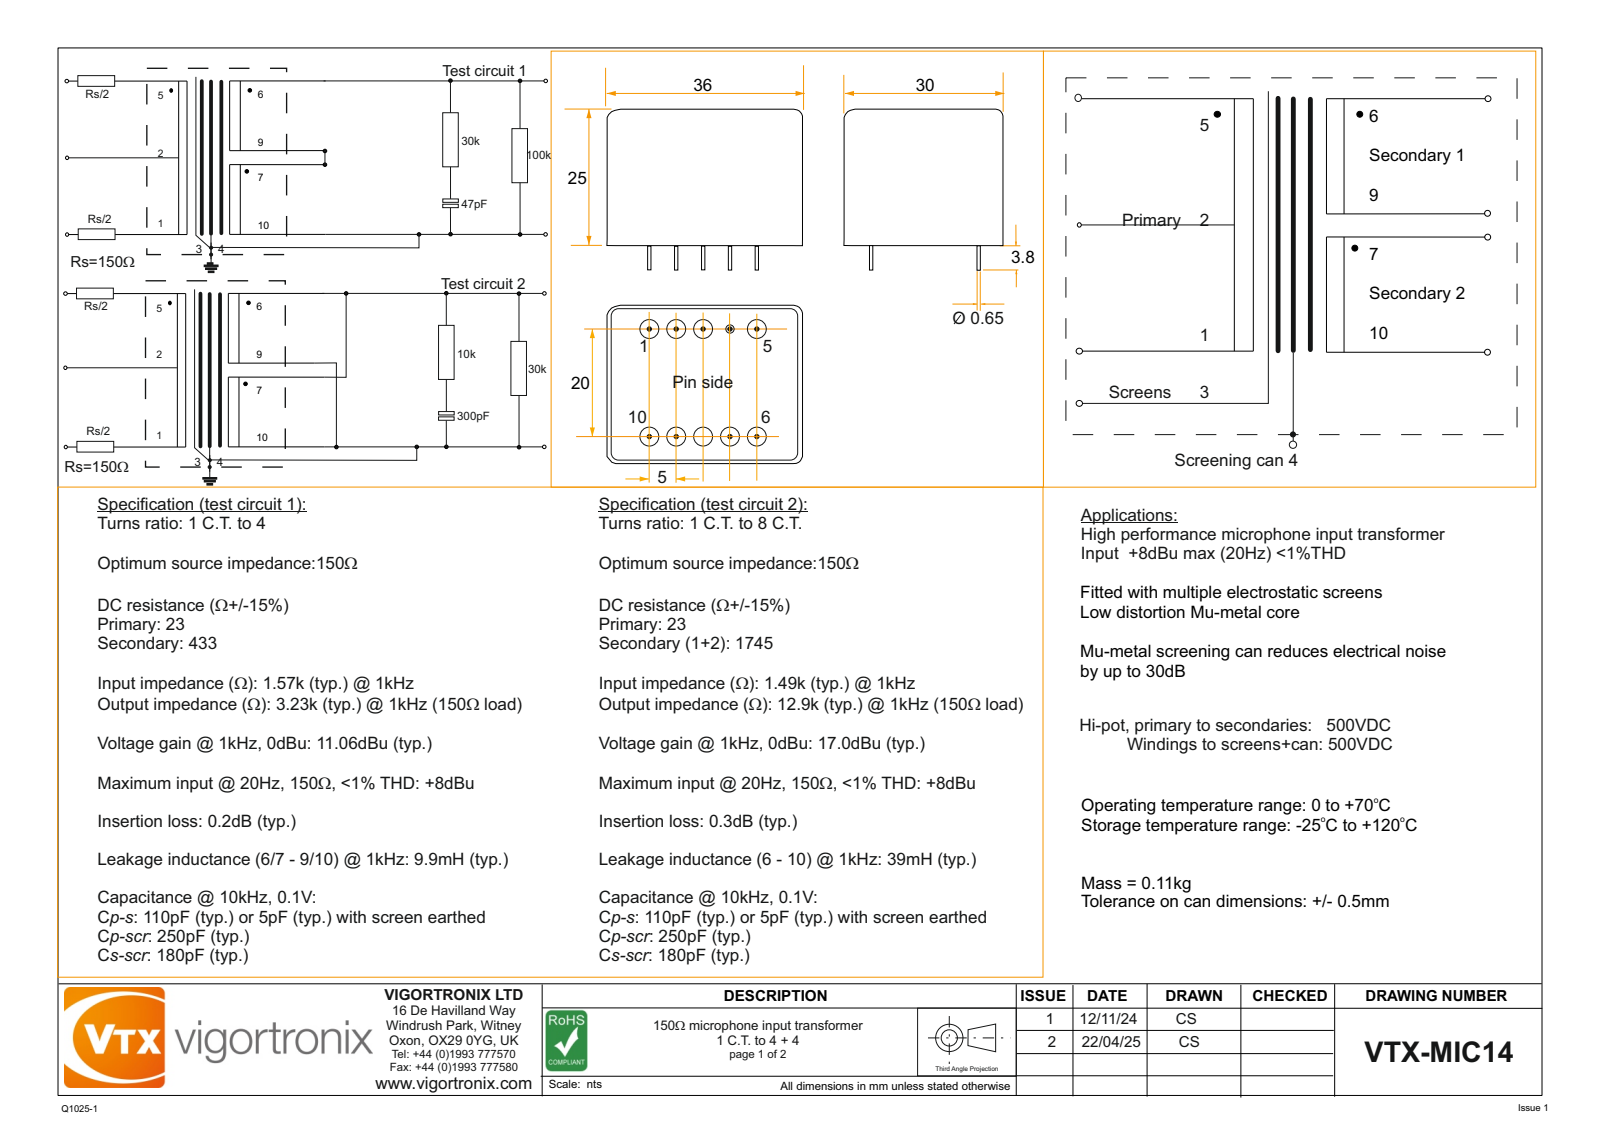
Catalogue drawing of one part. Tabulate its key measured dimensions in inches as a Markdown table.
| quantity | value |
| --- | --- |
| part name | VTX-MIC14; VTX-MIC14 Can; VTX-MIC14 Lid; VTX-MIC14 BOBBIN |
| STEP written by | SolidWorks 2024 (AUTOMOTIVE_DESIGN) |
| units | inches |
| bodies | 3 solids, 110 faces (32 planar, 66 cylindrical, 12 other) |
| overall size | 1.417 × 1.181 × 1.134 |
| volume | 1.241 in³ |
| surface area | 21.64 in² |
| round holes (diameter × count) | 0.094 × 9, 0.059 × 1 |
| round bosses / shafts (diameter × count) | 0.026 × 9 |
| partial cylindrical surfaces (radius × count) | 0.039 × 8, 0.091 × 8, 0.118 × 8, 0.098 × 4 |
| main face-to-face distances | 0.028, 0.02, 0.126, 0.106, 0.913, 0.894, 0.787, 0.043, 0.957, 0.937 |
| hole center spacings | 0.197, 0.812, 0.787, 0.394, 0.88, 0.591, 0.984, 1.113 |
